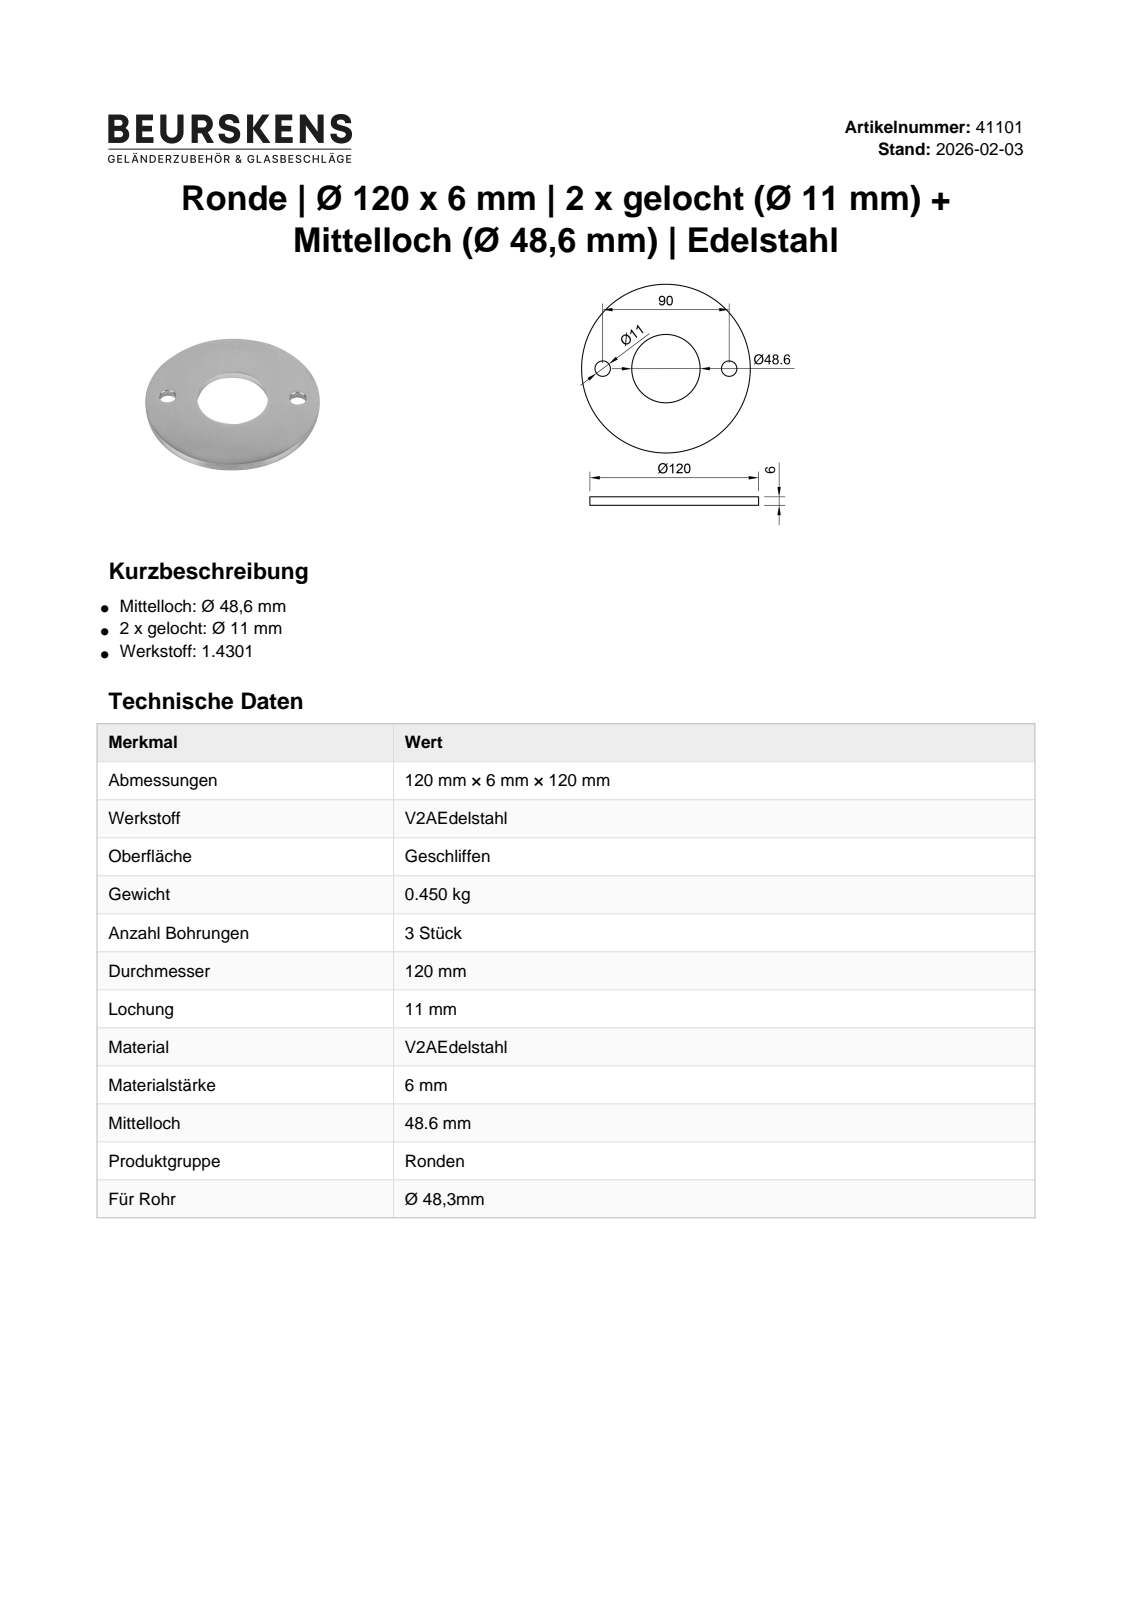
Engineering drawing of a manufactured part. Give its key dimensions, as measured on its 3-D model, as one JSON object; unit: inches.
{"part_name": "41101", "step_written_by": "Autodesk Inventor 2022 (AUTOMOTIVE_DESIGN)", "units": "inches", "bodies": {"solids": 1, "faces": 6, "planar": 2, "cylindrical": 4, "other": 0}, "overall_size": [4.724, 4.724, 0.236], "volume_in3": 3.392, "surface_area_in2": 34.29, "round_holes": [[0.433, 2], [1.913, 1]], "round_bosses_or_shafts": [[4.724, 1]], "face_to_face_distances": [0.236], "hole_center_spacings": [1.772, 3.543]}
